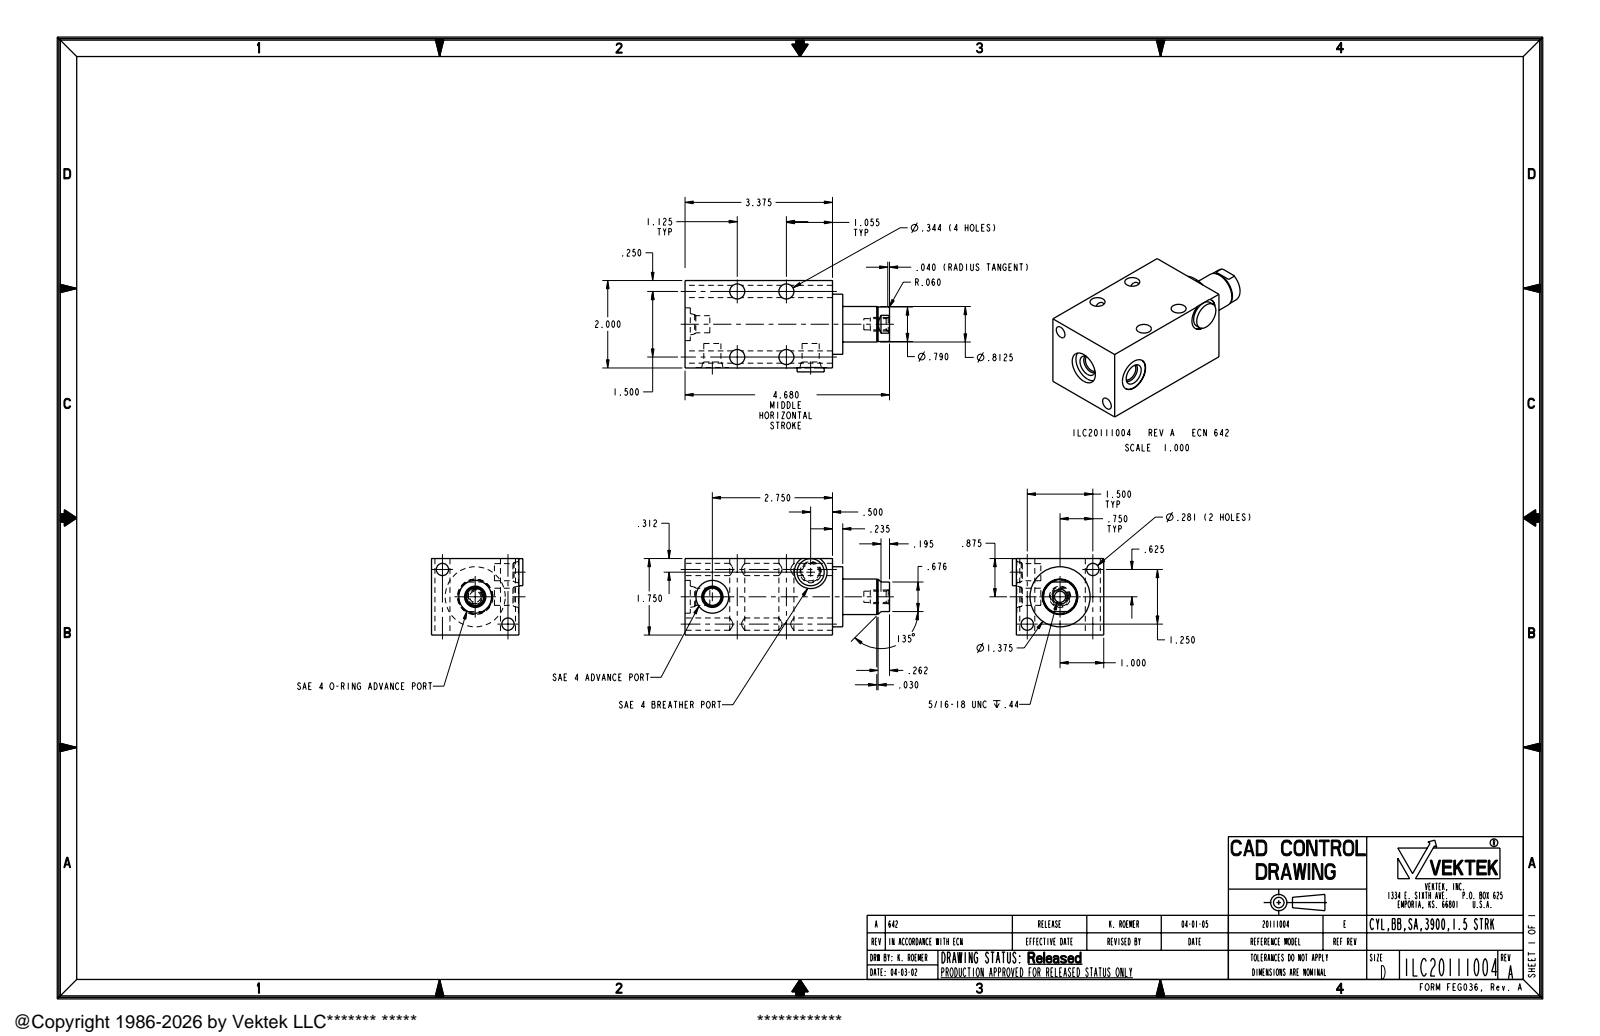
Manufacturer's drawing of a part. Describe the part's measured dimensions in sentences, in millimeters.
The part is named "ILC20111004". Its 3-D file was written by "PRO/ENGINEER BY PARAMETRIC TECHNOLOGY CORPORATION, 2004290 (AUTOMOTIVE_DESIGN_CC2)". It is 1 solid with 83 faces: 22 planar, 43 cylindrical and 18 other. Overall it measures 118.9 by 53.1 by 44.5 millimeters. Its volume is 187 500 cubic millimeters and its surface area 32 630 square millimeters. Round holes: 4 of diameter 8.7, 3 of diameter 10, 3 of diameter 19.1, 2 of diameter 7.1, 1 of diameter 6.5. Round bosses or shafts: 1 of diameter 34.9, 1 of diameter 20.7, 1 of diameter 20.1, 1 of diameter 15.7, 1 of diameter 7.9. The main face-to-face distances are 44.5, 50.8, 85.7, 6, 91.7, 50.5, 27.2, 33.1, 118.9, 2.3. The hole center spacings are 24.8, 28.6, 38.1, 47.6, 49.6, 58.9.
